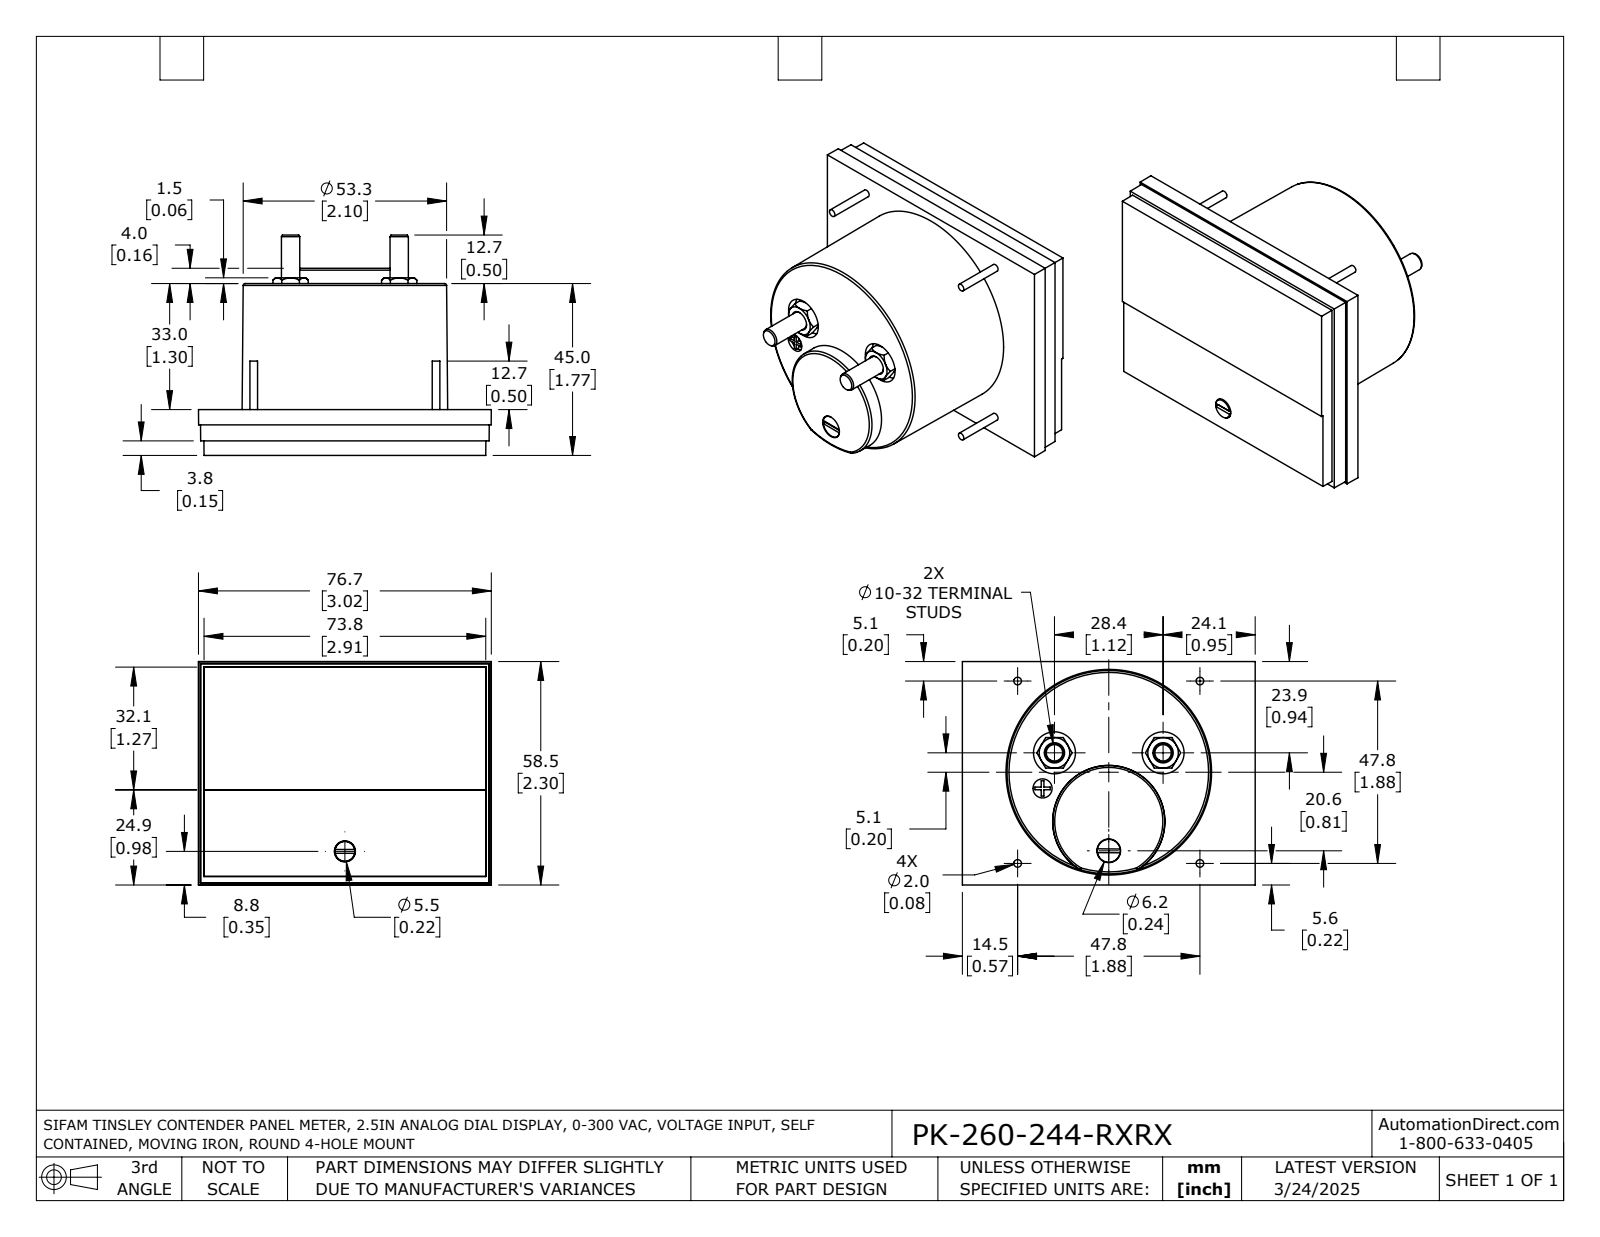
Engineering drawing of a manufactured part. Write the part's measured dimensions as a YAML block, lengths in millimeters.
part_name: "PK-260-244-RXRX"
step_written_by: "SolidWorks 2021 (AUTOMOTIVE_DESIGN)"
units: millimeters
bodies: {solids: 1, faces: 192, planar: 95, cylindrical: 37, other: 60}
overall_size: [76.7, 58.5, 57.7]
volume: 125500
surface_area: 23580
round_holes:
  - {diameter: 5, count: 3}
  - {diameter: 11, count: 2}
  - {diameter: 5.3, count: 1}
  - {diameter: 5.5, count: 1}
  - {diameter: 6.2, count: 1}
round_bosses_or_shafts:
  - {diameter: 2, count: 4}
  - {diameter: 4.8, count: 2}
  - {diameter: 6, count: 1}
  - {diameter: 5.2, count: 1}
partial_cylinders:
  - {radius: 0.8, count: 1}
face_to_face_distances: [0.5, 12, 3.3, 8.2, 3.8, 11.5, 1.4, 2, 10.1, 1.9]
hole_center_spacings: [29.3, 29.5, 9.8, 23.8, 23.9, 28.4, 32.9]
